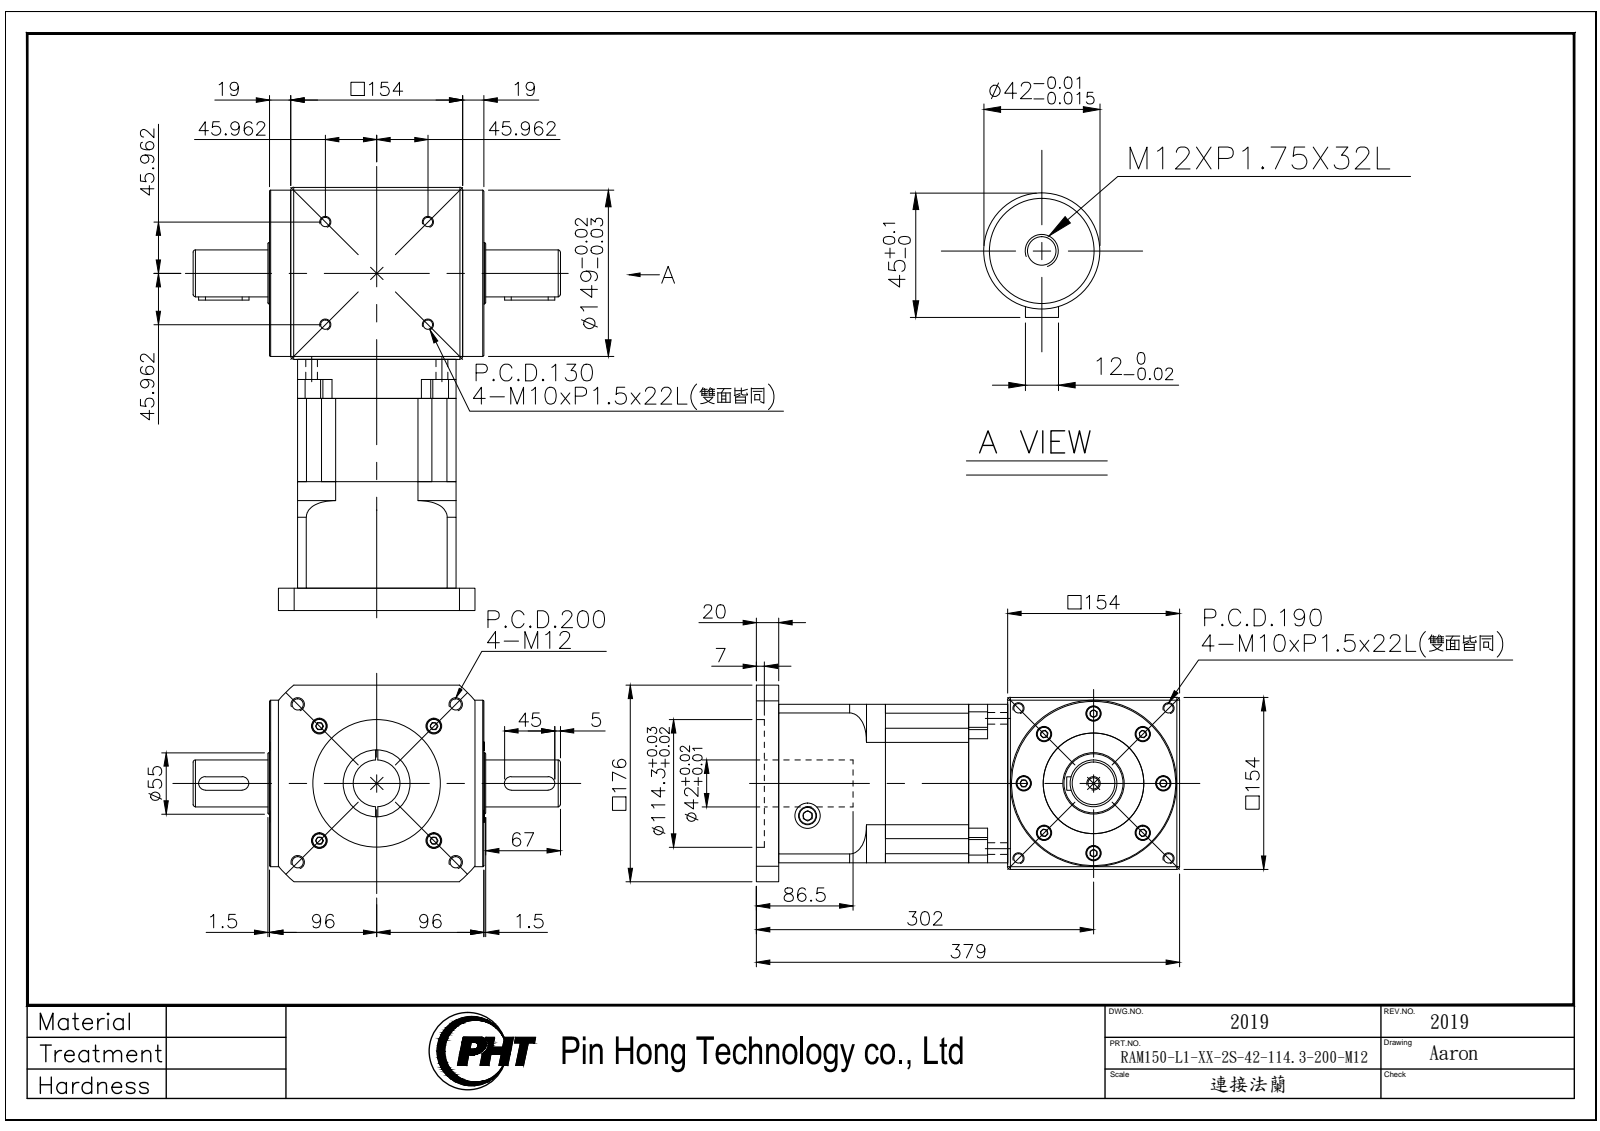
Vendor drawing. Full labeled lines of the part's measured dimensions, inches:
Part name (STEP PRODUCT): RAM150-L2-XX-2S-42-114.3-200-M12_2019
STEP written by: SolidWorks 2016 (AUTOMOTIVE_DESIGN)
Units: inches
Bodies: 6 solids, 910 faces (422 planar, 324 cylindrical, 164 other)
Overall size (bounding box): 14.921 × 12.953 × 6.929
Volume: 517.1 in³ · Surface area: 910 in²
Round holes (diameter × count): ⌀0.335 ×12, ⌀0.354 ×12, ⌀0.551 ×12, ⌀0.433 ×8, ⌀0.689 ×8, ⌀0.402 ×5, ⌀0.268 ×4, ⌀0.413 ×4, ⌀0.886 ×2, ⌀0.161 ×1, ⌀1.654 ×1, ⌀2.362 ×1
Round bosses / shafts (diameter × count): ⌀0.63 ×12, ⌀0.512 ×4, ⌀5.866 ×1, ⌀5.118 ×1, ⌀3.543 ×1, ⌀2.913 ×1, ⌀2.165 ×1, ⌀1.654 ×1
Partial cylindrical surfaces — rounded edges, fillets, slot ends (radius × count): R0.236 ×4, R0.394 ×4, R3.15 ×1, R3.74 ×1, R4.228 ×1, R4.528 ×1
Main face-to-face distances: 0.236, 5.827, 6.063, 5.591, 2.933, 4.311, 1.378, 0.984, 10.374, 7.441
Hole centre spacings: 2.795, 0.737, 0.74, 0.908, 1.433, 1.883, 2.651, 3.265
